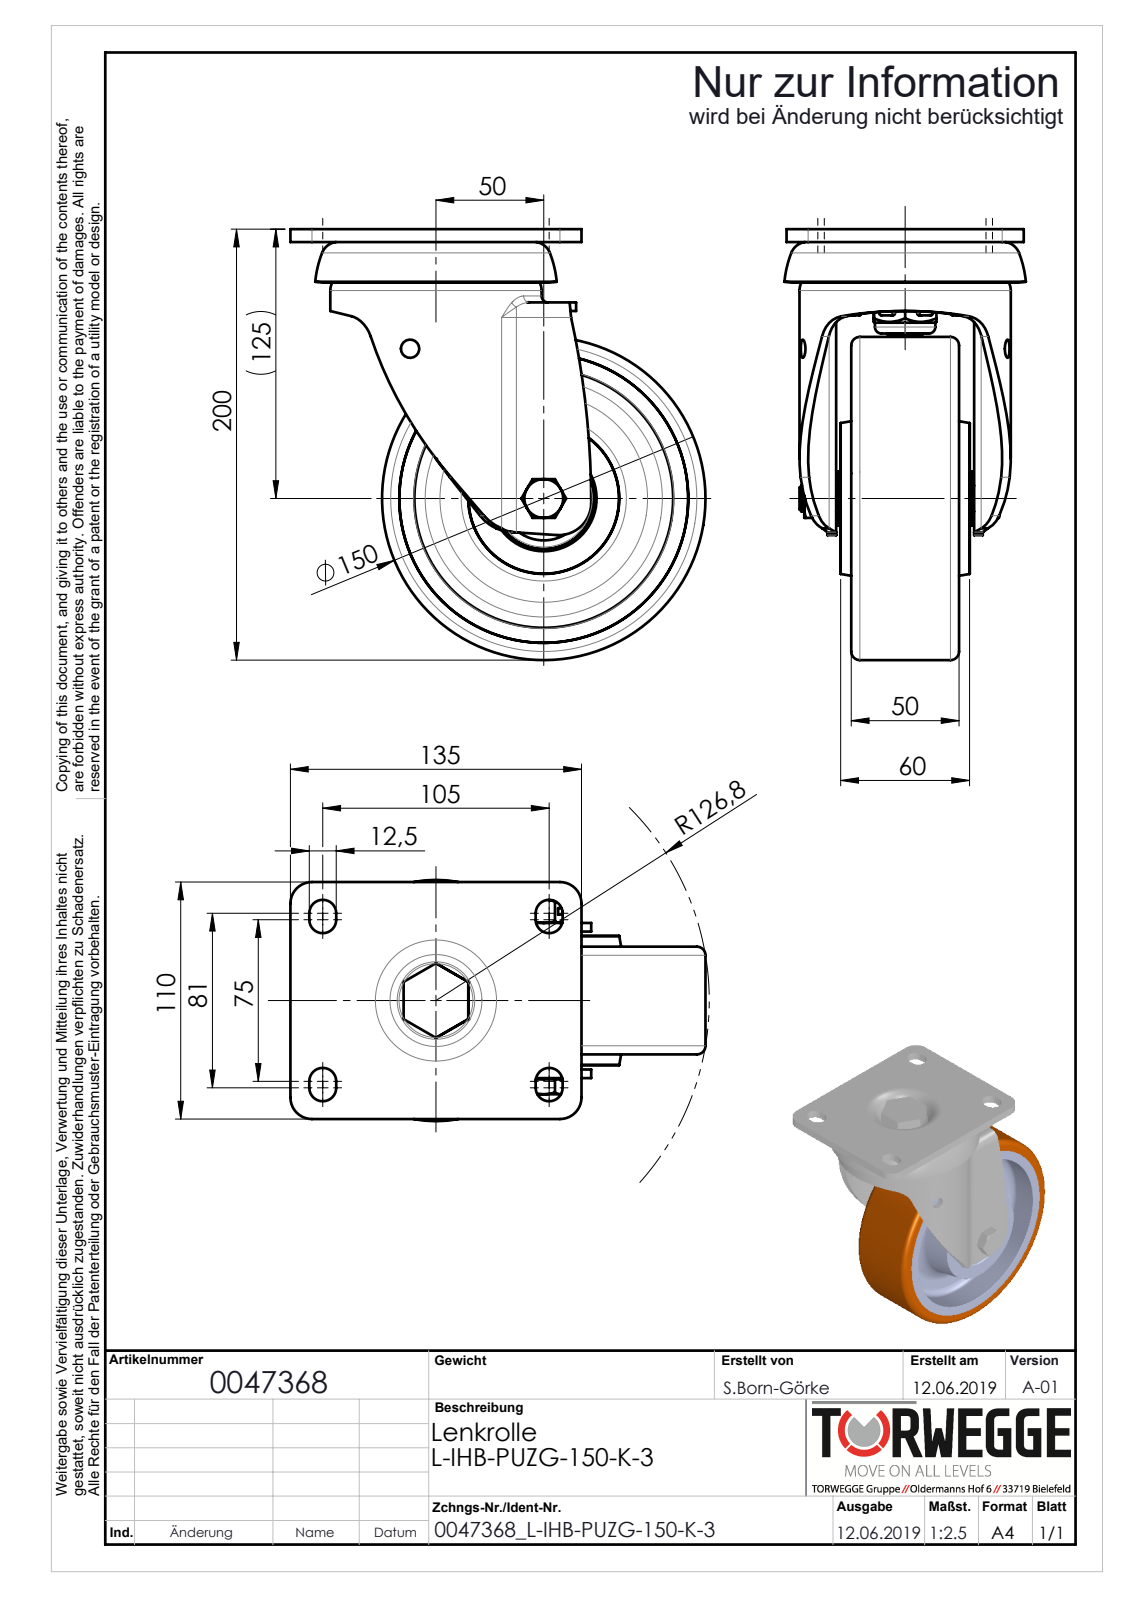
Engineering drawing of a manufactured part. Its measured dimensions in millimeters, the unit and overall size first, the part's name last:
Units: millimetres
Overall size (bounding box): 200 × 192.5 × 112
Round holes (diameter × count): ⌀8.5 ×1, ⌀10.2 ×1, ⌀12 ×1, ⌀12.2 ×1, ⌀12.5 ×1, ⌀20 ×1, ⌀21 ×1, ⌀38.9 ×1, ⌀75 ×1, ⌀120 ×1, ⌀134 ×1
Round bosses / shafts (diameter × count): ⌀150 ×1, ⌀98 ×1, ⌀28.1 ×1, ⌀25 ×1, ⌀20 ×1, ⌀19.9 ×1, ⌀18 ×1
Partial cylindrical surfaces — rounded edges, fillets, slot ends (radius × count): R1 ×21, R6.25 ×8, R10 ×4, R15 ×3, R3 ×2, R7 ×2, R11 ×2, R14 ×2
Main face-to-face distances: 6, 33, 61, 4, 11, 2, 68, 7, 57, 5
Hole centre spacings: 93.14
Bodies: 0 solids, 463 faces (157 planar, 143 cylindrical, 163 other)
Part name (STEP PRODUCT): 0047368_L-IHB-PUZG-150-K-3_(A-01)
STEP written by: SolidWorks 2018 (AUTOMOTIVE_DESIGN)
